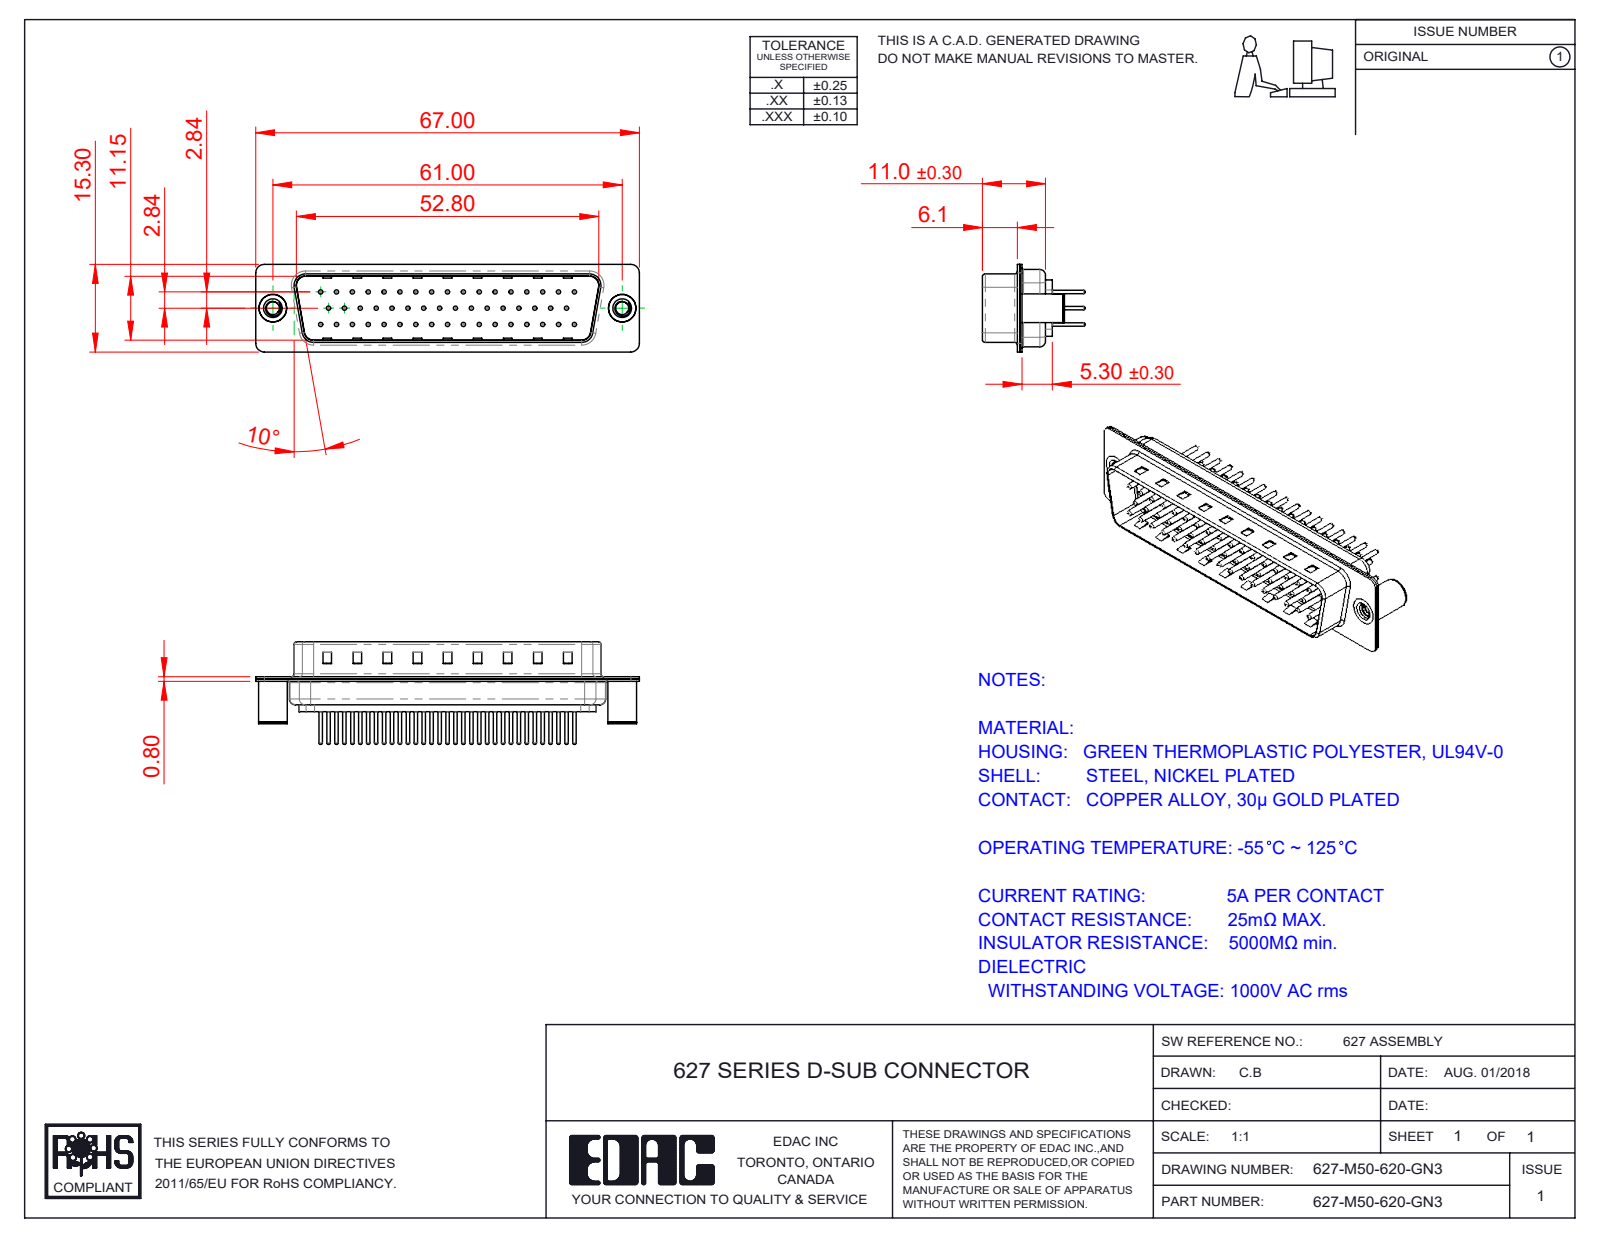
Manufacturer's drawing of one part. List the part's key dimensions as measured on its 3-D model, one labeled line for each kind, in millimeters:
Part name (STEP PRODUCT): 627M Housing_50 Contacts; 627-M50-620-GN3; 627M Shell Rear_50 Contacts; 627M 4-40 Threaded Board Spacer (+4 more)
STEP written by: SolidWorks 2020 (CONFIG_CONTROL_DESIGN)
Units: millimetres
Bodies: 55 solids, 2296 faces (553 planar, 865 cylindrical, 878 other)
Overall size (bounding box): 67 × 17.9 × 15.3
Volume: 4 648 mm³ · Surface area: 10 957 mm²
Round holes (diameter × count): ⌀0.75 ×50, ⌀1.6 ×50, ⌀2 ×50, ⌀2.26 ×2, ⌀3.26 ×2, ⌀4 ×2, ⌀4.8 ×2
Round bosses / shafts (diameter × count): ⌀1.5 ×50, ⌀0.6 ×50, ⌀5 ×2, ⌀4.9 ×2
Partial cylindrical surfaces — rounded edges, fillets, slot ends (radius × count): R1.5 ×16, R2 ×12, R0.5 ×8, R1.6 ×8, R0.25 ×4, R0.6 ×4, R0.65 ×4, R0.9 ×4
Main face-to-face distances: 0.4, 11.55, 5.7, 6.1, 0.78, 0.77, 12.33, 5.3, 12.32, 13.1
Hole centre spacings: 3.16, 2.77, 5.54, 8.31, 11.08, 13.85, 16.62, 5.03
